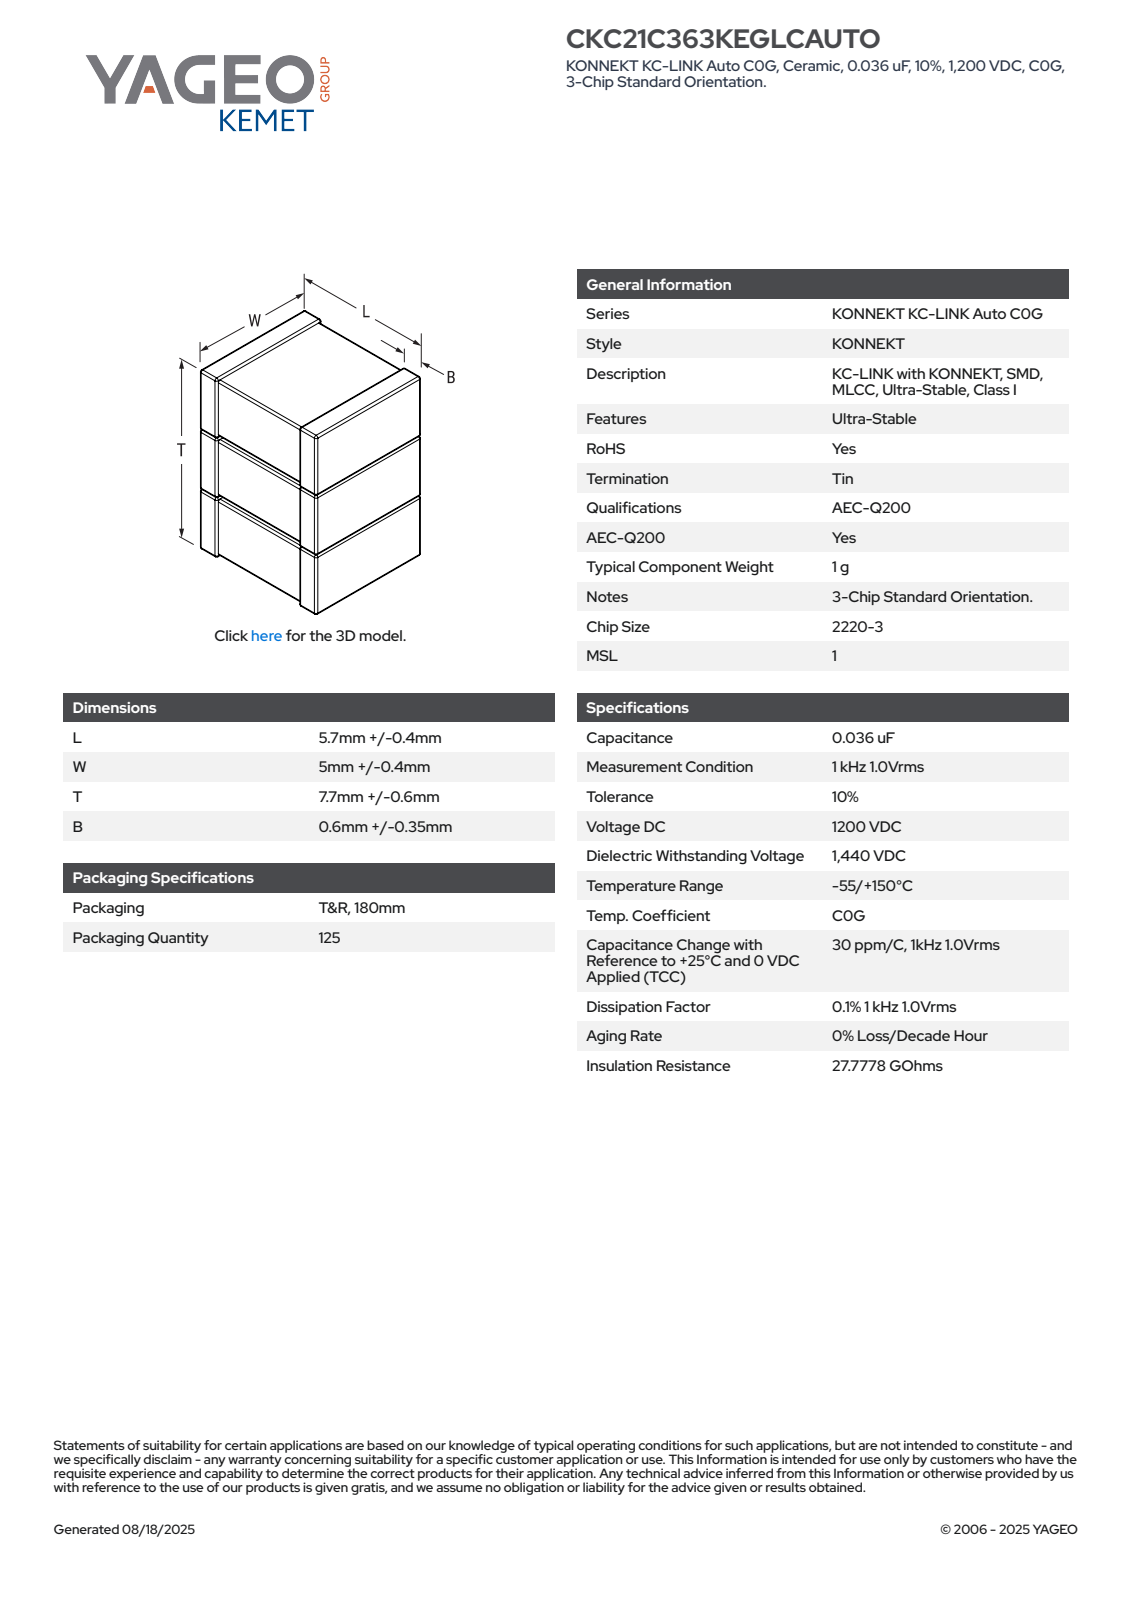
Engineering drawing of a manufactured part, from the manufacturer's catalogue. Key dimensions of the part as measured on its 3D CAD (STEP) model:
Part name (STEP PRODUCT): CCSS_K3T_2220-3_L6.1W5.4B0.95T8.3
STEP written by: SolidWorks 2021 (AUTOMOTIVE_DESIGN)
Units: millimetres
Bodies: 6 solids, 243 faces (99 planar, 96 cylindrical, 48 other)
Overall size (bounding box): 8.3 × 6.1 × 5.4
Volume: 255 mm³ · Surface area: 380 mm²
Main face-to-face distances: 2.77, 5.53, 2.76, 2.68, 5.44, 2.59, 5.35, 6.1, 2.85, 2.67
